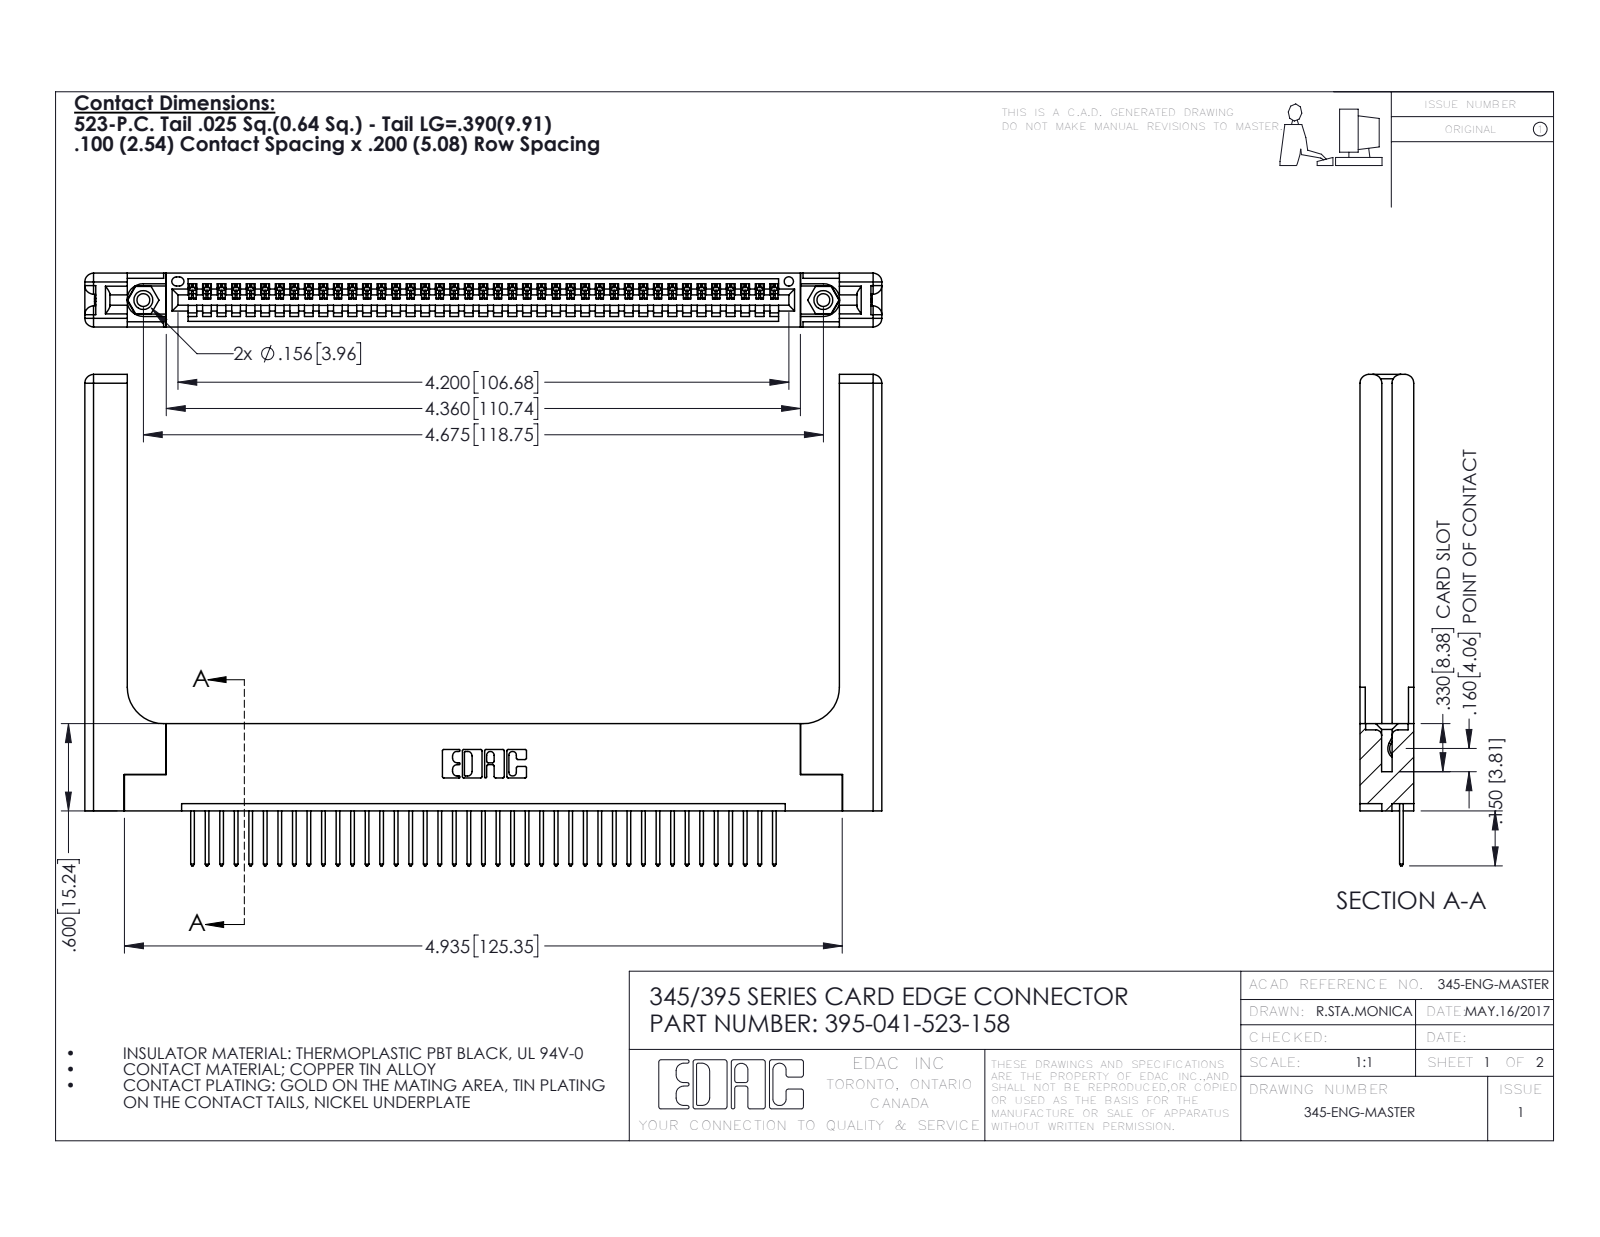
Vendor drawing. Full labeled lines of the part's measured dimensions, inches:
Part name (STEP PRODUCT): 395-041-523-158; 345 Part_Flush Mounting Lugs - 0.156 Dia-TH; 345-220-058_345-220-058; 345-250-001_345-250-001-102 (+1 more)
STEP written by: SolidWorks 2016 (CONFIG_CONTROL_DESIGN)
Units: inches
Bodies: 46 solids, 2760 faces (1868 planar, 832 cylindrical, 60 other)
Overall size (bounding box): 5.479 × 3.377 × 0.37
Volume: 1.324 in³ · Surface area: 35.45 in²
Round holes (diameter × count): ⌀0.089 ×2, ⌀0.125 ×2, ⌀0.156 ×2, ⌀0.064 ×1
Round bosses / shafts (diameter × count): ⌀0.155 ×2
Partial cylindrical surfaces — rounded edges, fillets, slot ends (radius × count): R0.006 ×82, R0.01 ×82, R0.01 ×22, R0.06 ×16, R0.007 ×6, R0.031 ×6, R0.026 ×3, R0.03 ×2
Main face-to-face distances: 0.072, 0.37, 0.298, 0.2, 0.098, 0.272, 0.025, 0.148, 0.15, 0.225
Hole centre spacings: 0.27, 4.439, 4.675
